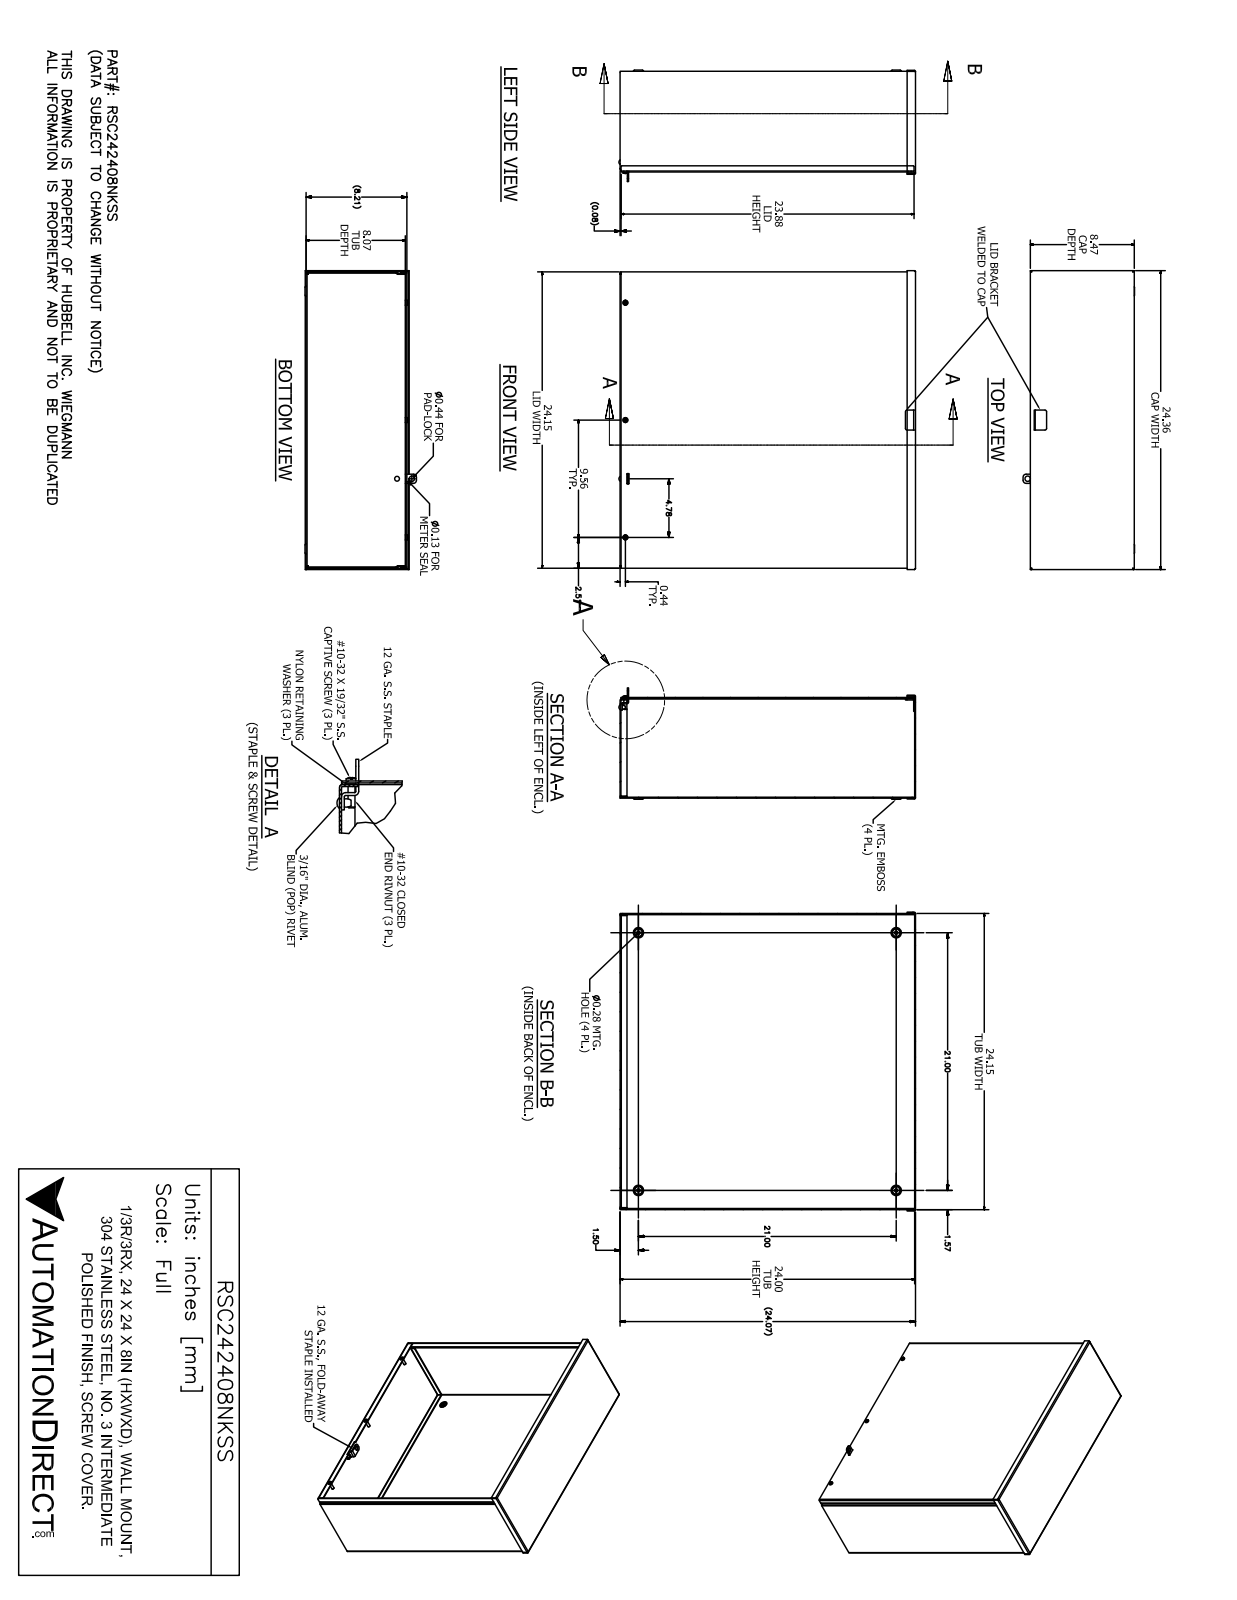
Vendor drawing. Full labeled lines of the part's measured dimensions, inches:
Part name (STEP PRODUCT): RSC242408NKSS
STEP written by: SolidWorks 2017 (AUTOMOTIVE_DESIGN)
Units: inches
Bodies: 16 solids, 458 faces (237 planar, 113 cylindrical, 108 other)
Overall size (bounding box): 24.359 × 24.164 × 9.084
Volume: 150.4 in³ · Surface area: 4 096 in²
Round holes (diameter × count): ⌀0.25 ×6, ⌀0.281 ×4, ⌀0.156 ×3, ⌀0.196 ×3, ⌀0.257 ×3, ⌀0.278 ×3, ⌀0.125 ×1, ⌀0.198 ×1, ⌀0.201 ×1, ⌀0.437 ×1
Round bosses / shafts (diameter × count): ⌀0.453 ×3, ⌀0.406 ×3, ⌀0.248 ×3, ⌀0.167 ×3, ⌀0.187 ×1
Partial cylindrical surfaces — rounded edges, fillets, slot ends (radius × count): R0.031 ×23, R0.105 ×17, R0.125 ×4, R0.25 ×4, R0.062 ×3, R0.089 ×3, R0.047 ×2, R0.05 ×2
Main face-to-face distances: 0.074, 8.132, 8.206, 8.058, 24, 24.074, 23.926, 24.148, 0.115, 23.959
Hole centre spacings: 9.563, 21, 25.053, 23.156, 1.417, 1.441, 10.554, 10.557
